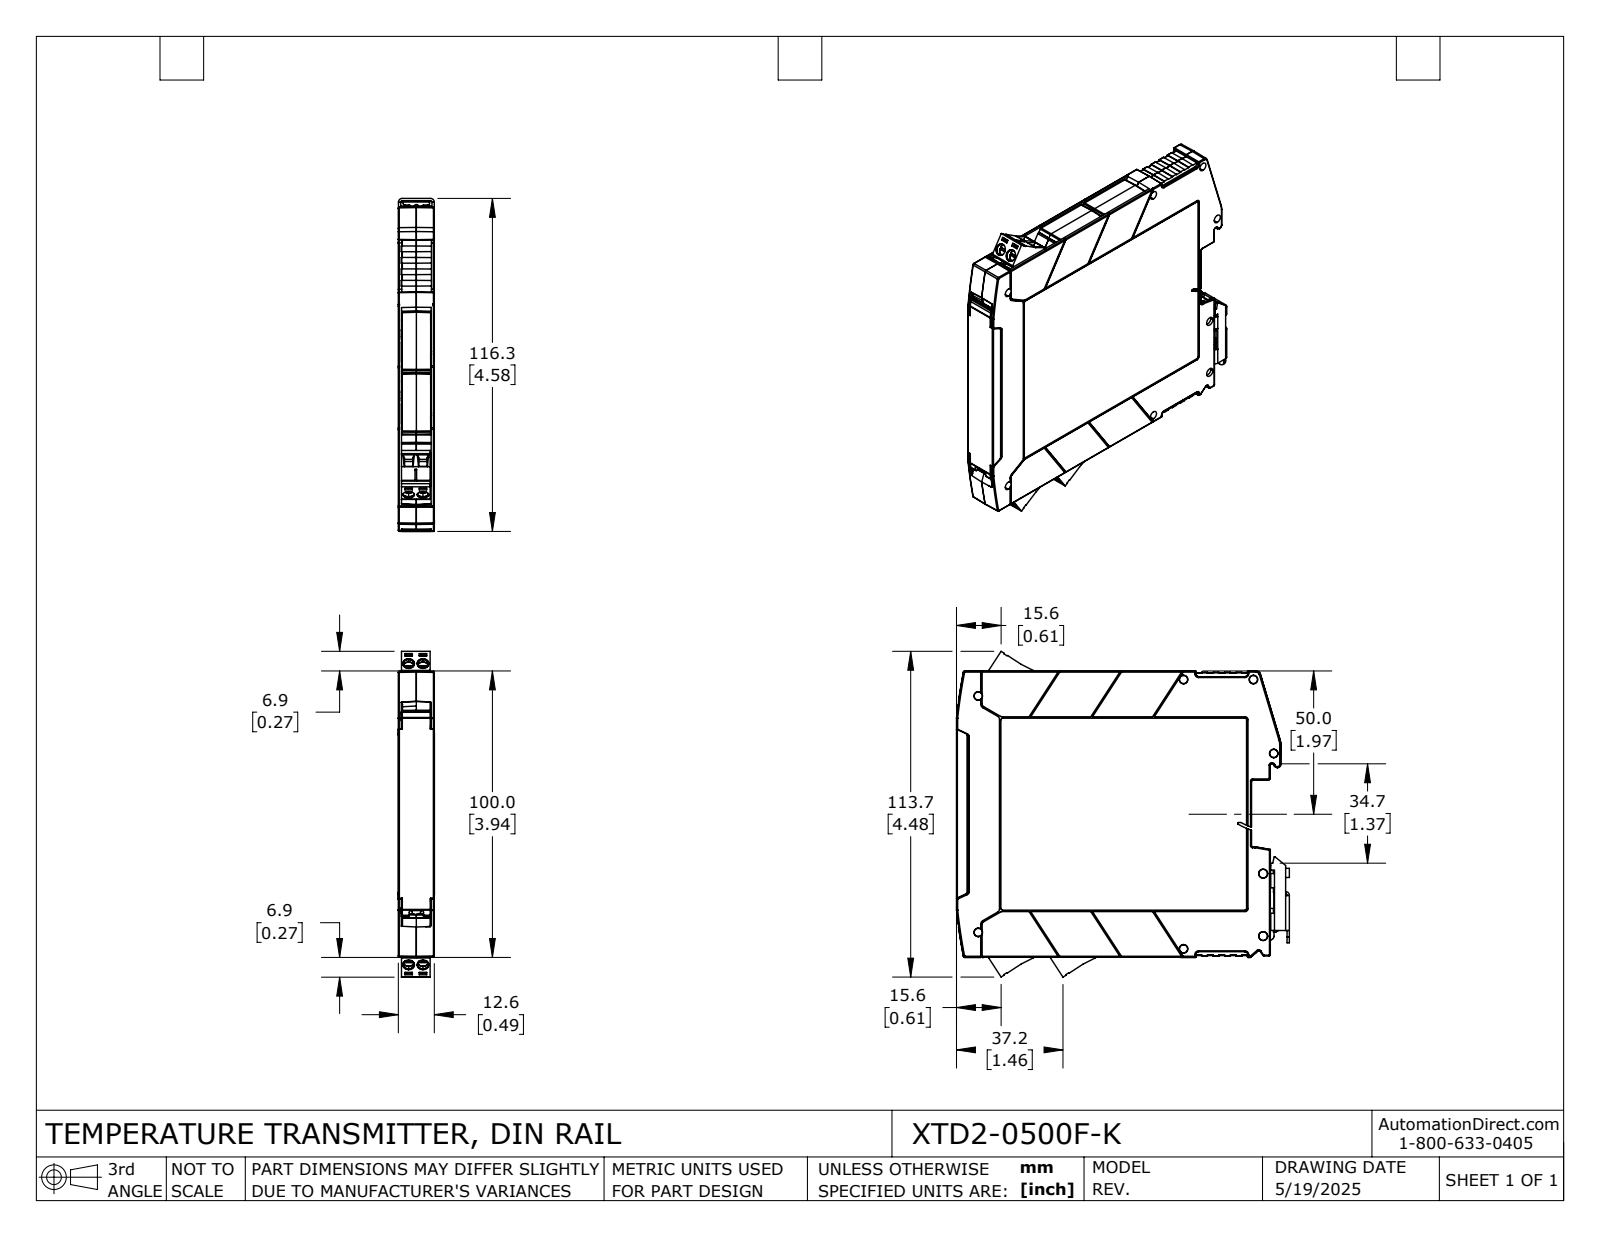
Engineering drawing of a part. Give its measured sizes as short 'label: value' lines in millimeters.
name: XTD2-0500F-K
written by: SolidWorks 2024 (AUTOMOTIVE_DESIGN)
unit: mm
bodies: 14 solids, 3337 faces (1910 planar, 596 cylindrical, 831 other)
size: 116.3 × 113.7 × 12.6
volume: 39 490 mm³; area: 65 480 mm²
holes: 6× ⌀1.6, 6× ⌀2.8, 6× ⌀3.9, 6× ⌀4
bosses: 6× ⌀4, 6× ⌀2.5, 2× ⌀1.5, 2× ⌀1.3
rounds: 89× R0.2, 78× R0.3, 71× R0.5, 22× R1, 20× R0.1, 13× R0.4, 12× R0.2, 8× R0.7
face distances: 1.2, 11.3, 12.5, 10.1, 1.1, 11.5, 10.2, 0.8, 5, 6.3
hole spacings: 5, 11.8, 12.8, 18.1, 18.8
